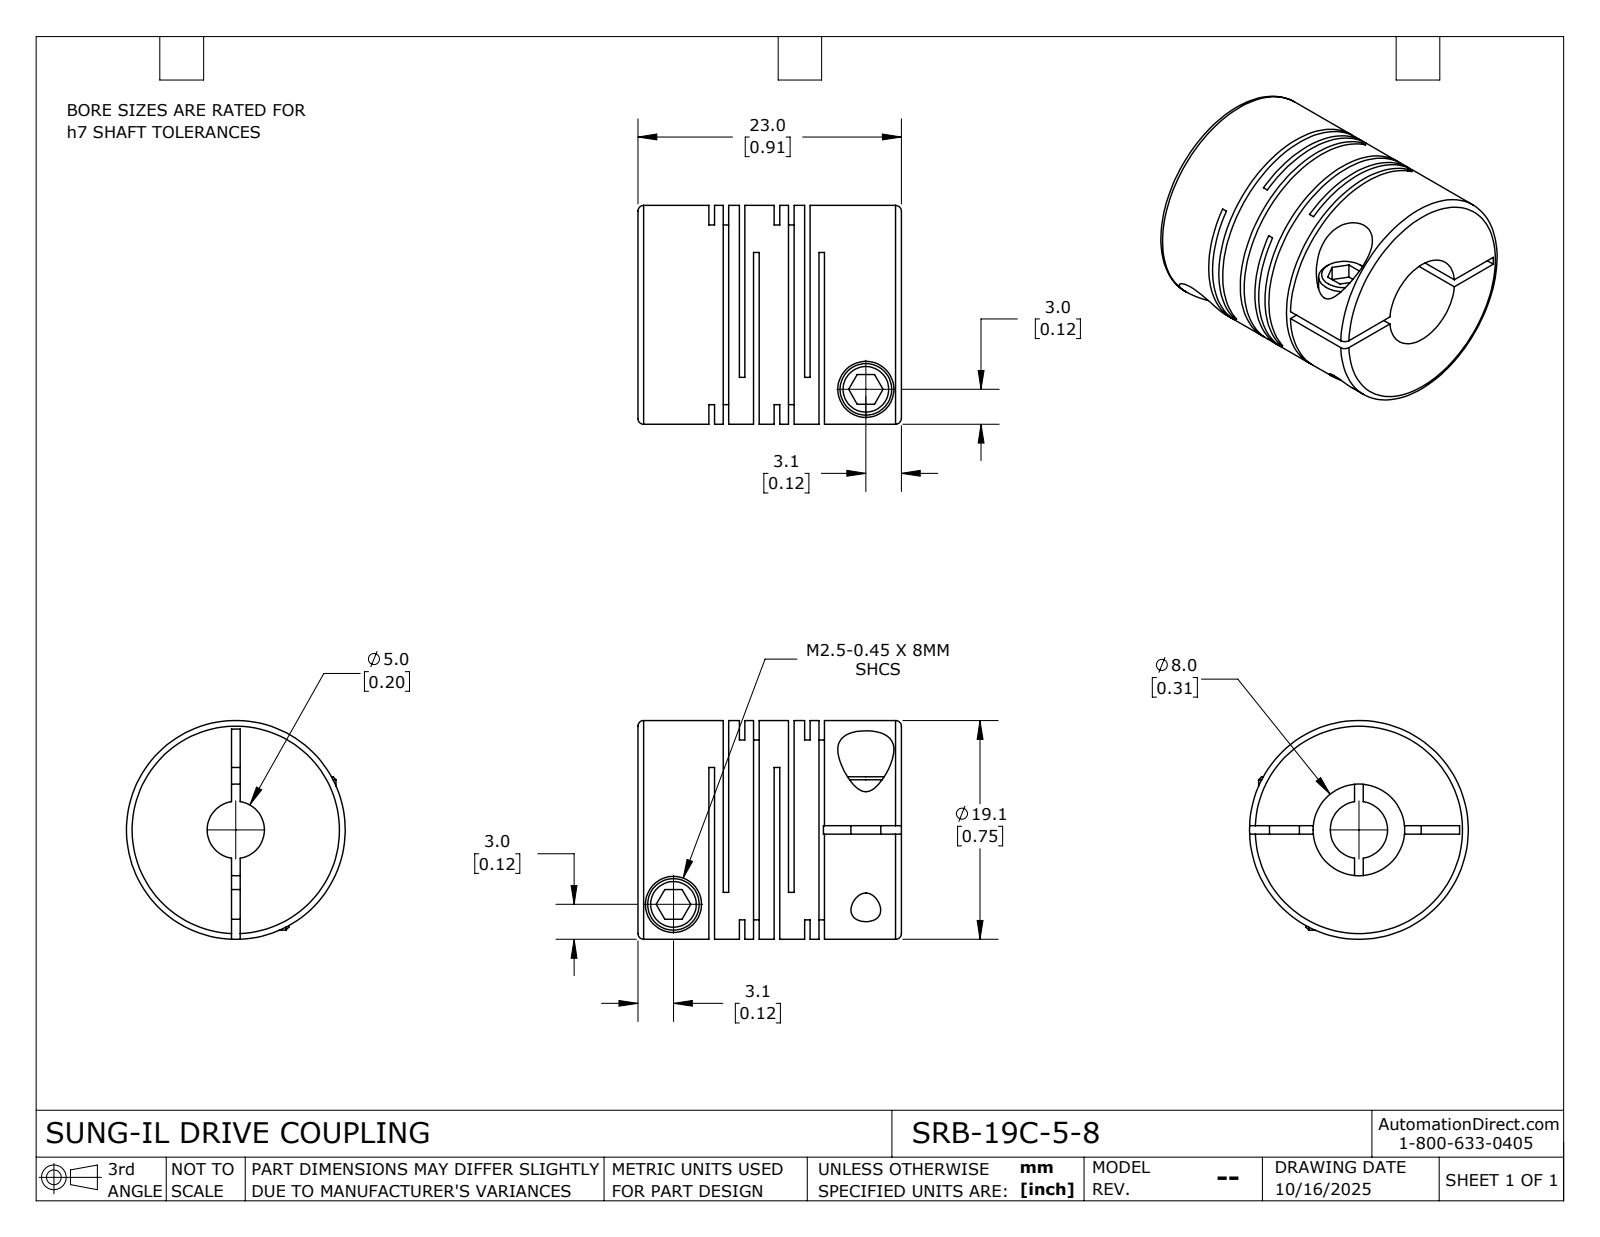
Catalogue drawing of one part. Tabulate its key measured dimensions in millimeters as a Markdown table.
| quantity | value |
| --- | --- |
| part name | SRB-19C-5-8 |
| STEP written by | SolidWorks 2024 (CONFIG_CONTROL_DESIGN) |
| units | millimeters |
| bodies | 1 solid, 115 faces (60 planar, 42 cylindrical, 13 other) |
| overall size | 23 × 19.1 × 19.1 |
| volume | 4 652 mm³ |
| surface area | 5 728 mm² |
| round holes (diameter × count) | 2.6 × 2, 4.9 × 2, 5 × 1, 8 × 1 |
| round bosses / shafts (diameter × count) | 4.5 × 2, 19.1 × 1 |
| main face-to-face distances | 2.65, 0.48, 5.7, 1.25, 2.17, 3.05, 5.22, 0.77, 4.45, 1.4 |
